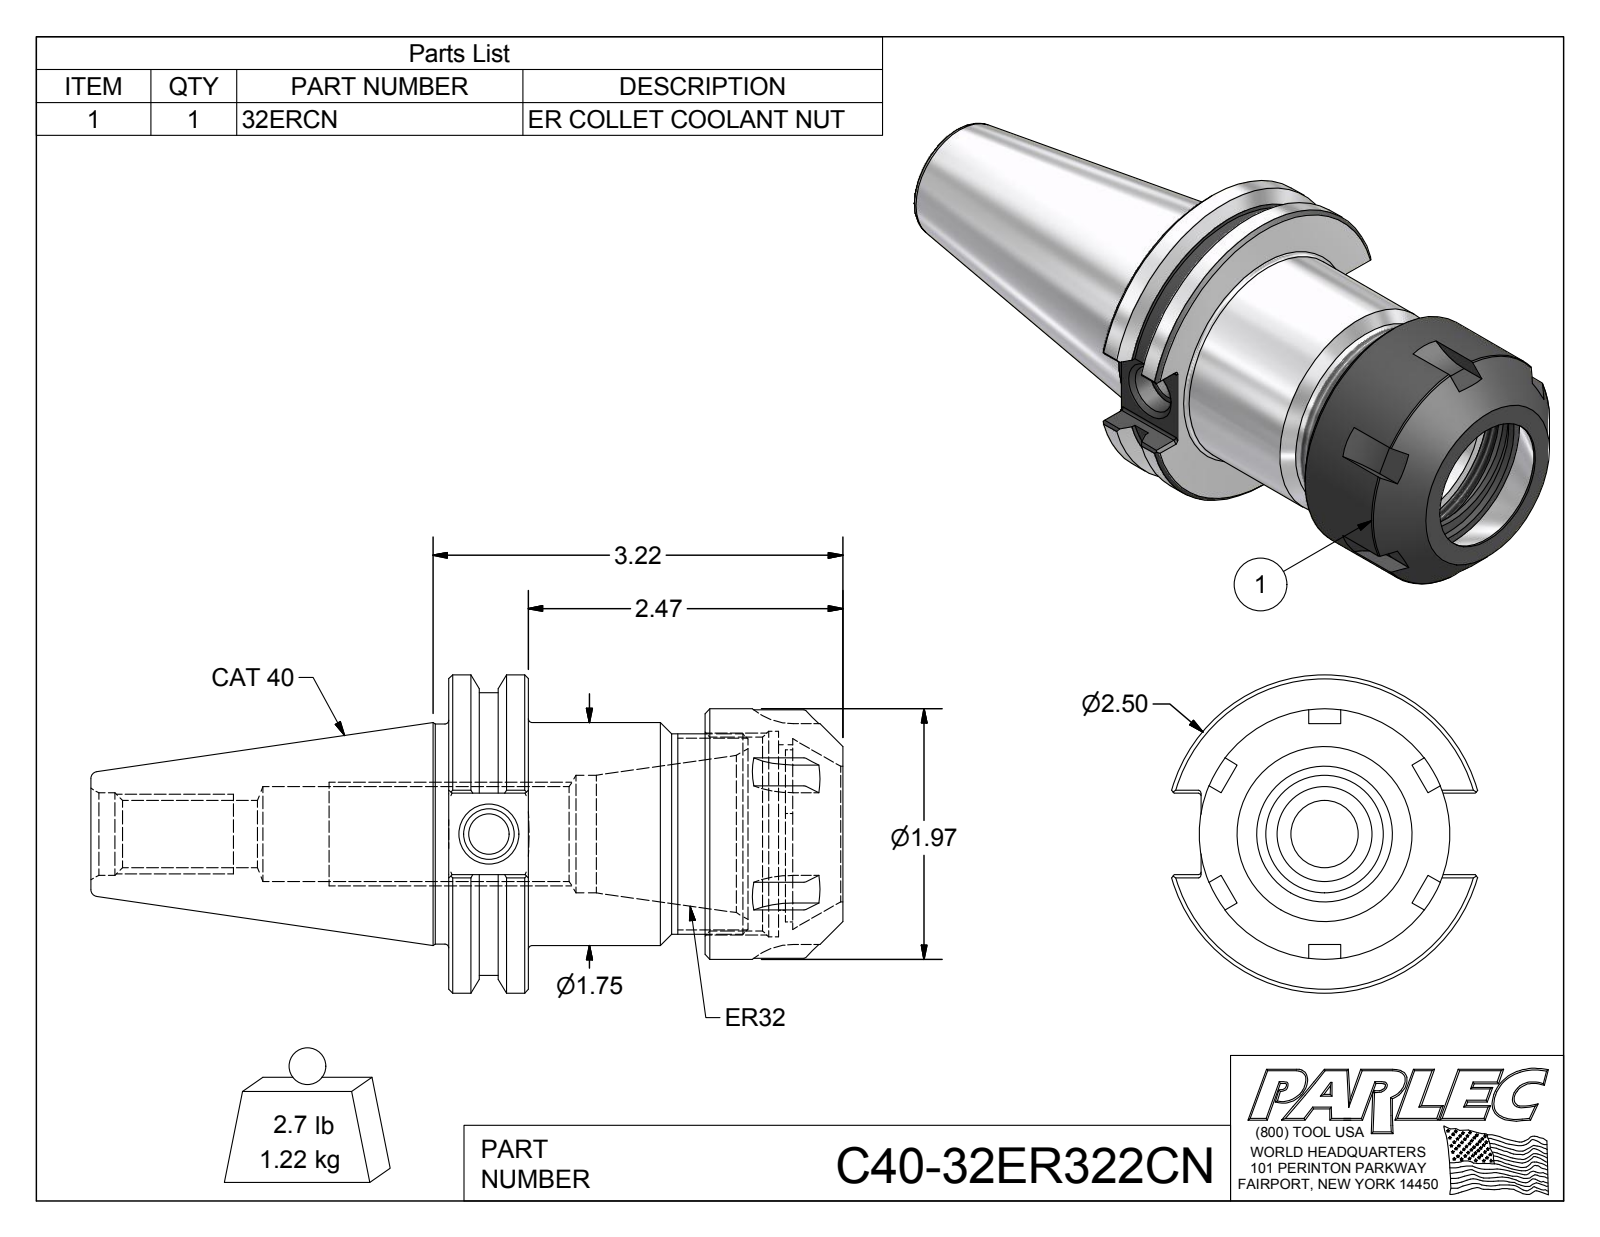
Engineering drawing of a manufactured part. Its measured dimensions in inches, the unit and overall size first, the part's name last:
Units: inches
Overall size (bounding box): 5.908 × 2.5 × 2.403
Round holes (diameter × count): ⌀0.315 ×1, ⌀0.399 ×1, ⌀0.527 ×1, ⌀0.648 ×1, ⌀0.745 ×1, ⌀0.925 ×1, ⌀1.063 ×1, ⌀1.299 ×1, ⌀1.522 ×1, ⌀1.614 ×1
Round bosses / shafts (diameter × count): ⌀2.5 ×1, ⌀2.219 ×1, ⌀1.969 ×1, ⌀1.75 ×1, ⌀1.73 ×1, ⌀1.575 ×1
Partial cylindrical surfaces — rounded edges, fillets, slot ends (radius × count): R0.02 ×12, R0.5 ×6, R0.689 ×1
Main face-to-face distances: 0.625, 2.012, 1.387, 2.591, 1.966, 0.579, 3.095, 2.47, 1.083, 0.504
Hole centre spacings: 0.059
Volume: 9.347 in³ · Surface area: 61.44 in²
Bodies: 2 solids, 127 faces (54 planar, 39 cylindrical, 34 other)
Part name (STEP PRODUCT): C40-32ER322CN; C40-32ER3-1; 32ERCN
STEP written by: Autodesk Inventor 2012 (AUTOMOTIVE_DESIGN)
